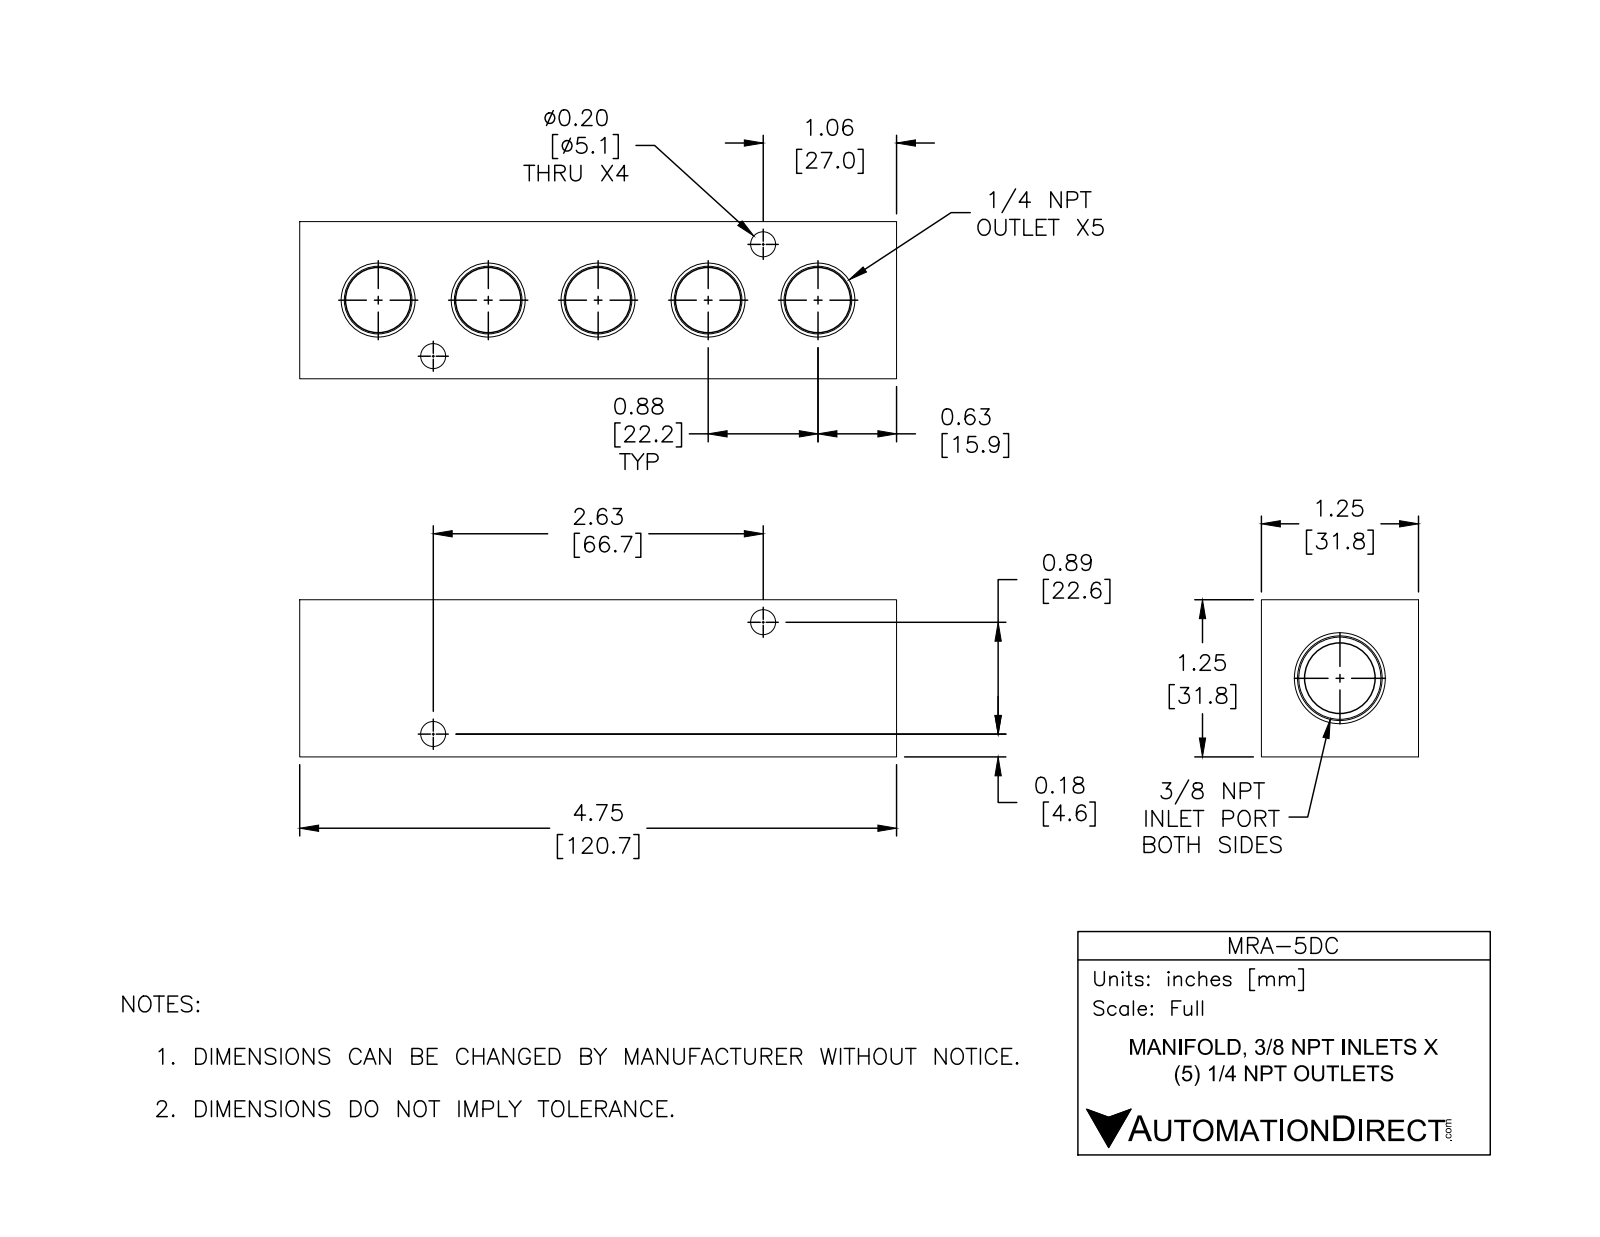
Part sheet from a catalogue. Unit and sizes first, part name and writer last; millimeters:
Units: millimetres
Overall size (bounding box): 120.7 × 31.8 × 31.8
Round holes (diameter × count): ⌀5.1 ×4, ⌀14.3 ×1
Partial cylindrical surfaces — rounded edges, fillets, slot ends (radius × count): R5.6 ×5
Main face-to-face distances: 31.8, 120.7, 21.8, 9.9, 10.4, 110.2, 99.8
Hole centre spacings: 70.4
Volume: 91 850 mm³ · Surface area: 24 920 mm²
Bodies: 1 solid, 74 faces (18 planar, 28 cylindrical, 28 other)
Part name (STEP PRODUCT): MRA-5DC
STEP written by: SolidWorks 2015 (CONFIG_CONTROL_DESIGN)
